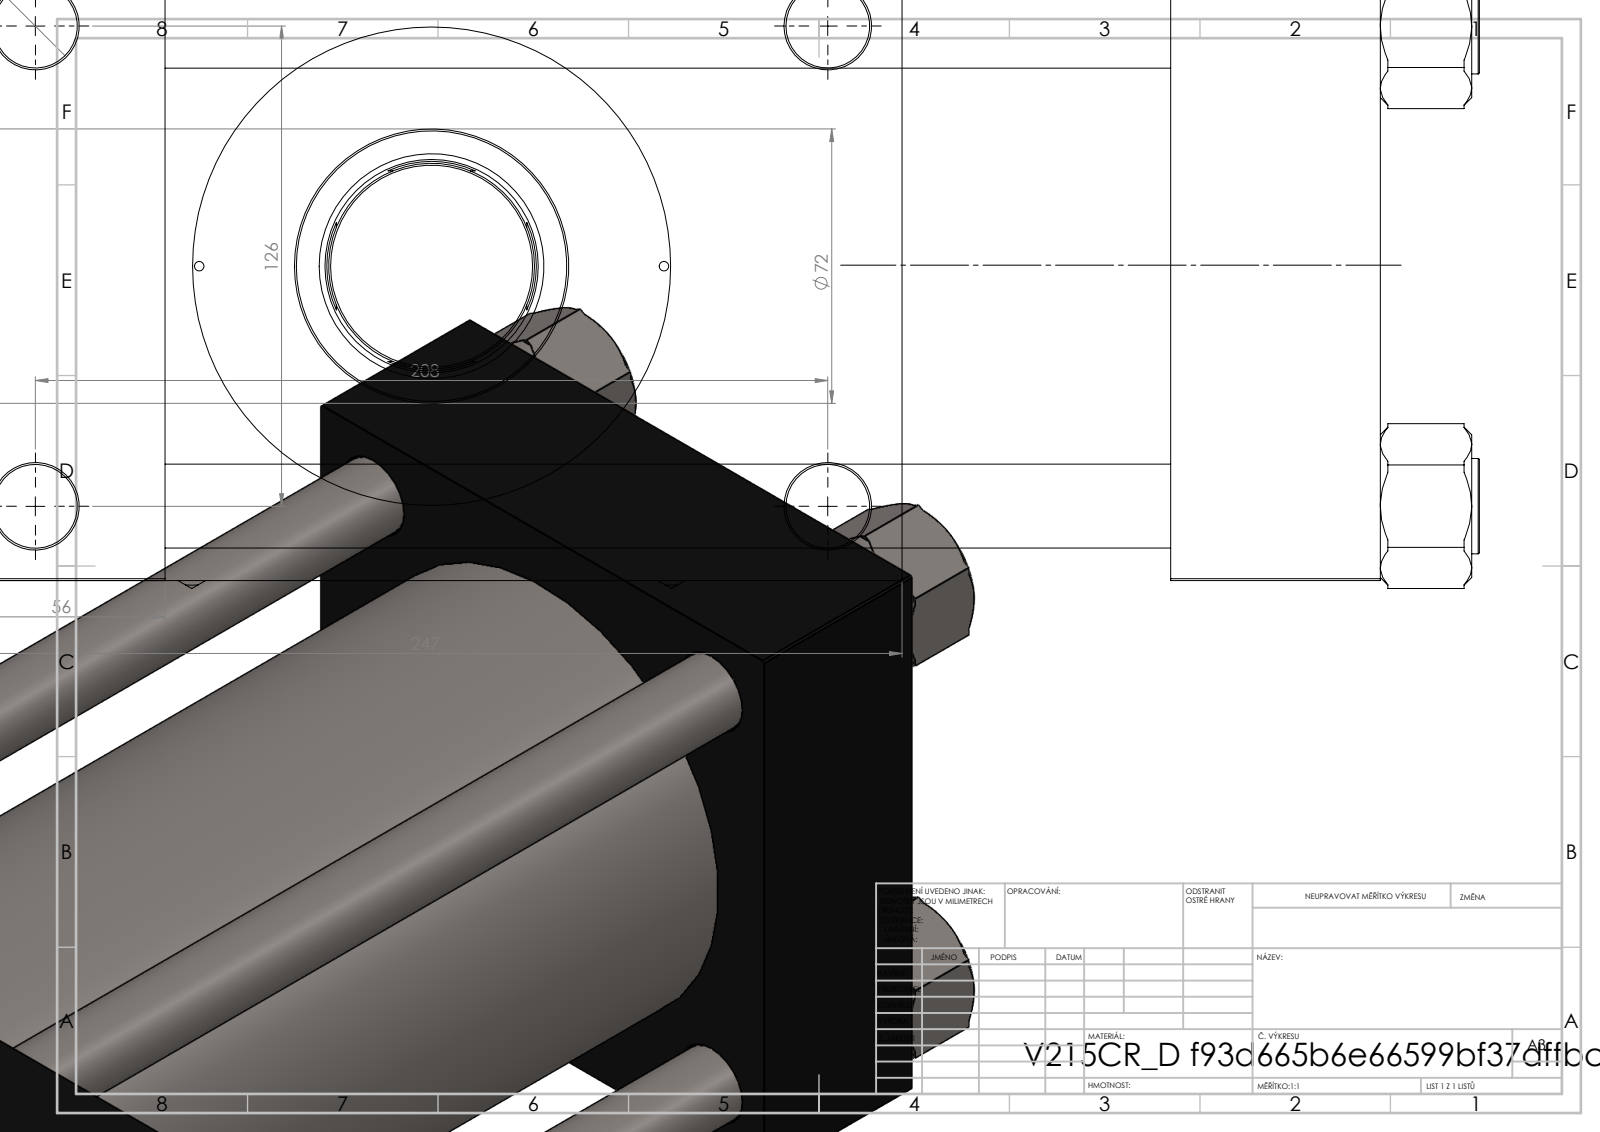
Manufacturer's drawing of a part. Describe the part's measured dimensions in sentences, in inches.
The part is named "V215CR_VCP_D; V215_VC_A; NUT_M5_D; V215CR_ROD_END_F (+2 more)". Its 3-D file was written by "SolidWorks 2019 (CONFIG_CONTROL_DESIGN)". It is 12 solids with 1168 faces: 550 planar, 94 cylindrical and 524 other. Overall it measures 20.079 by 9.724 by 6.659 inches. Its volume is 363.2 cubic inches and its surface area 1 198 square inches. Round holes: 8 of diameter 0.866, 2 of diameter 0.098, 2 of diameter 0.276, 2 of diameter 1.269, 2 of diameter 1.772, 1 of diameter 1.594, 1 of diameter 2.205, 1 of diameter 2.323, 1 of diameter 3.78, 1 of diameter 4.921, 1 of diameter 4.941. Round bosses or shafts: 4 of diameter 0.984, 1 of diameter 5.157, 1 of diameter 2.835, 1 of diameter 2.126, 1 of diameter 1.575. The main face-to-face distances are 6.496, 10.394, 2.165, 12.559, 2.205, 14.764, 12.598, 1.614, 8.11, 13.927. The hole center spacings are 1.616, 2.48, 3.003, 3.505, 4.787, 4.957, 5.215, 5.473.
